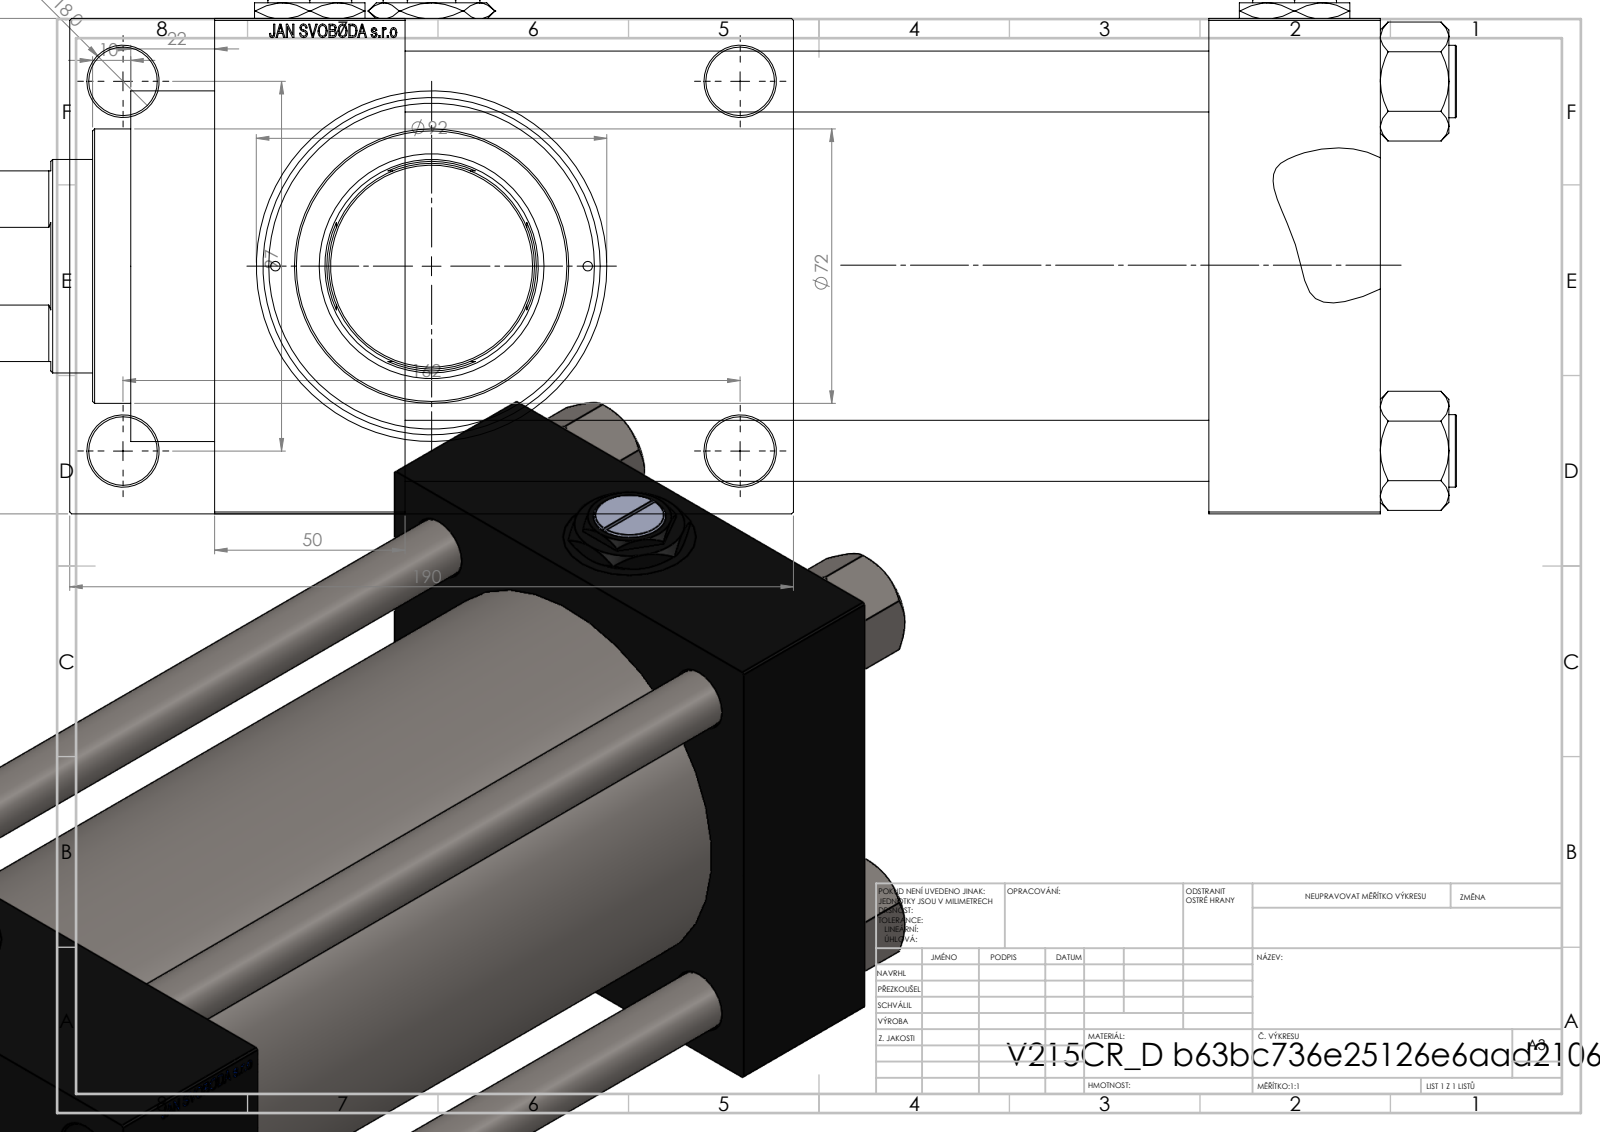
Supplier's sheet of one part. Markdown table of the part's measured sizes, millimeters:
| quantity | value |
| --- | --- |
| part name | Zatka_pro_OIL_PORT; V215CR_VCP_D; NUT_M5_D; V215CR_ROD_END_F (+3 more) |
| STEP written by | SolidWorks 2019 (CONFIG_CONTROL_DESIGN) |
| units | millimeters |
| bodies | 14 solids, 1274 faces (599 planar, 107 cylindrical, 568 other) |
| overall size | 435 × 190 × 137 |
| volume | 3 299 000 mm³ |
| surface area | 525 051 mm² |
| round holes (diameter × count) | 16 × 4, 18 × 4, 26.44 × 4, 35 × 4, 7 × 3, 2.5 × 2, 40.5 × 1, 56 × 1, 59 × 1, 76 × 1, 85.5 × 1, 100 × 1 |
| round bosses / shafts (diameter × count) | 19 × 4, 106 × 1, 92 × 1, 72 × 1, 54 × 1, 40 × 1 |
| main face-to-face distances | 130, 50, 45, 256, 211, 306, 261, 160, 30, 51 |
| hole center spacings | 32.55, 49.02, 62.87, 68.52, 94.41, 96.9, 101.73, 102.27 |
